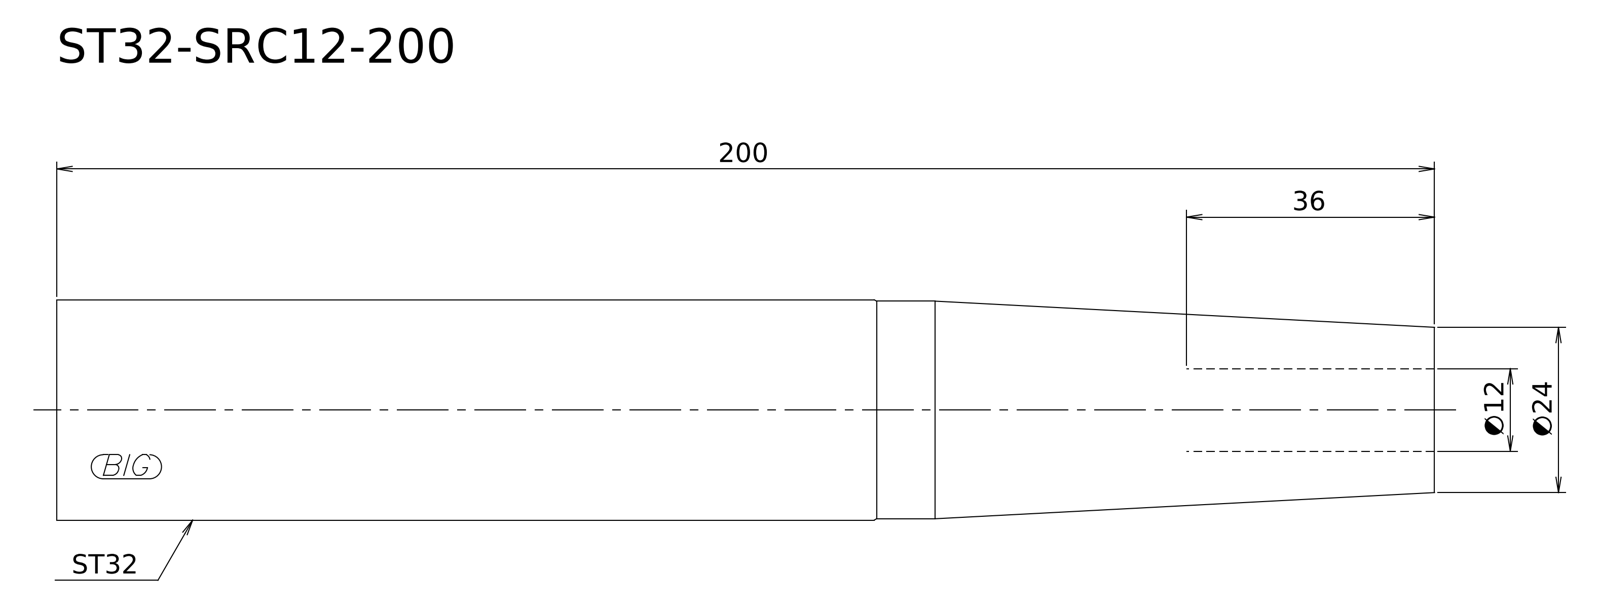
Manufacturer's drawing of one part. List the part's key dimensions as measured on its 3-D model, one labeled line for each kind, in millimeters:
STEP written by: Kubotek KeyCreator V8.5.1 (14335) (CONFIG_CONTROL_DESIGN)
Units: millimetres
Bodies: 1 solid, 6 faces (2 planar, 2 cylindrical, 2 other)
Overall size (bounding box): 200 × 32 × 32
Volume: 146 647 mm³ · Surface area: 20 409 mm²
Round bosses / shafts (diameter × count): ⌀32 ×1, ⌀31.6 ×1
Main face-to-face distances: 200
